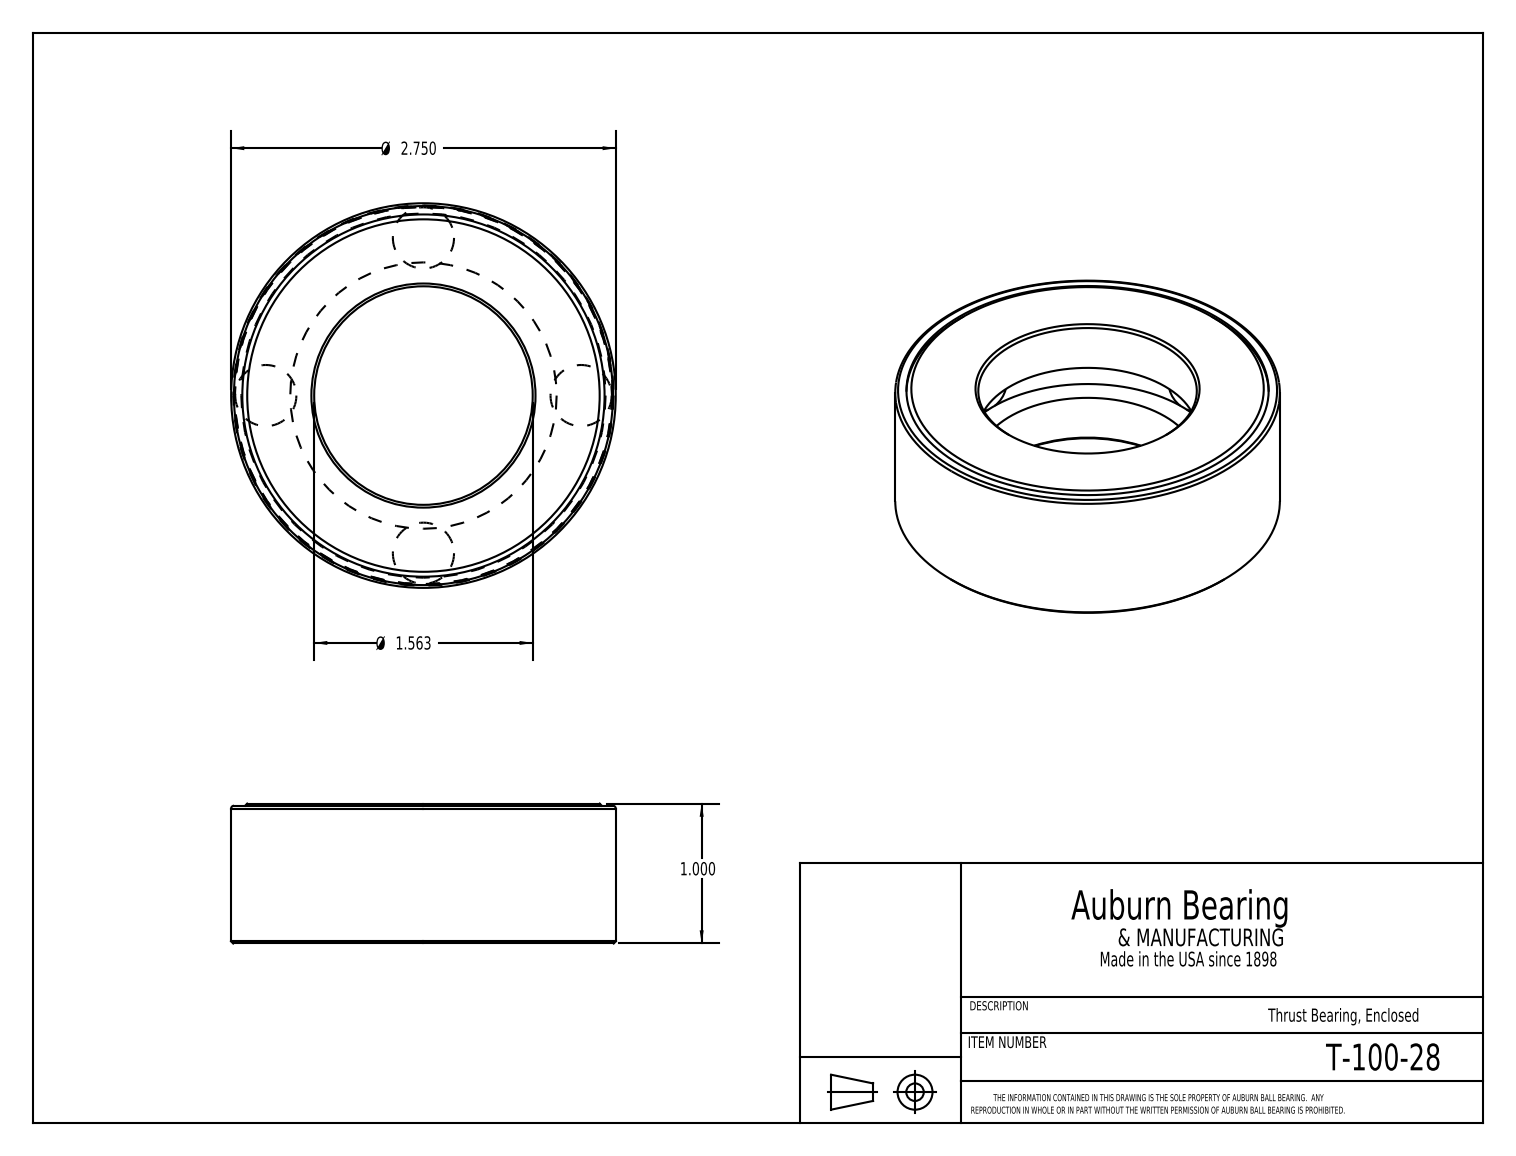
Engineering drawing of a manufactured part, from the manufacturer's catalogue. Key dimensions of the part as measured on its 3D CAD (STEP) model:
Part name (STEP PRODUCT): T-100-28
STEP written by: SolidWorks 2016 (CONFIG_CONTROL_DESIGN)
Units: inches
Bodies: 6 solids, 28 faces (9 planar, 7 cylindrical, 12 other)
Overall size (bounding box): 2.75 × 2.75 × 1
Volume: 2.833 in³ · Surface area: 39.66 in²
Round holes (diameter × count): ⌀1.563 ×1, ⌀2.59 ×1, ⌀2.71 ×1
Round bosses / shafts (diameter × count): ⌀2.75 ×1, ⌀2.696 ×1
Main face-to-face distances: 1, 0.369, 0.631, 0.262, 0.985, 0.616, 0.354, 0.015, 0.965, 0.596
